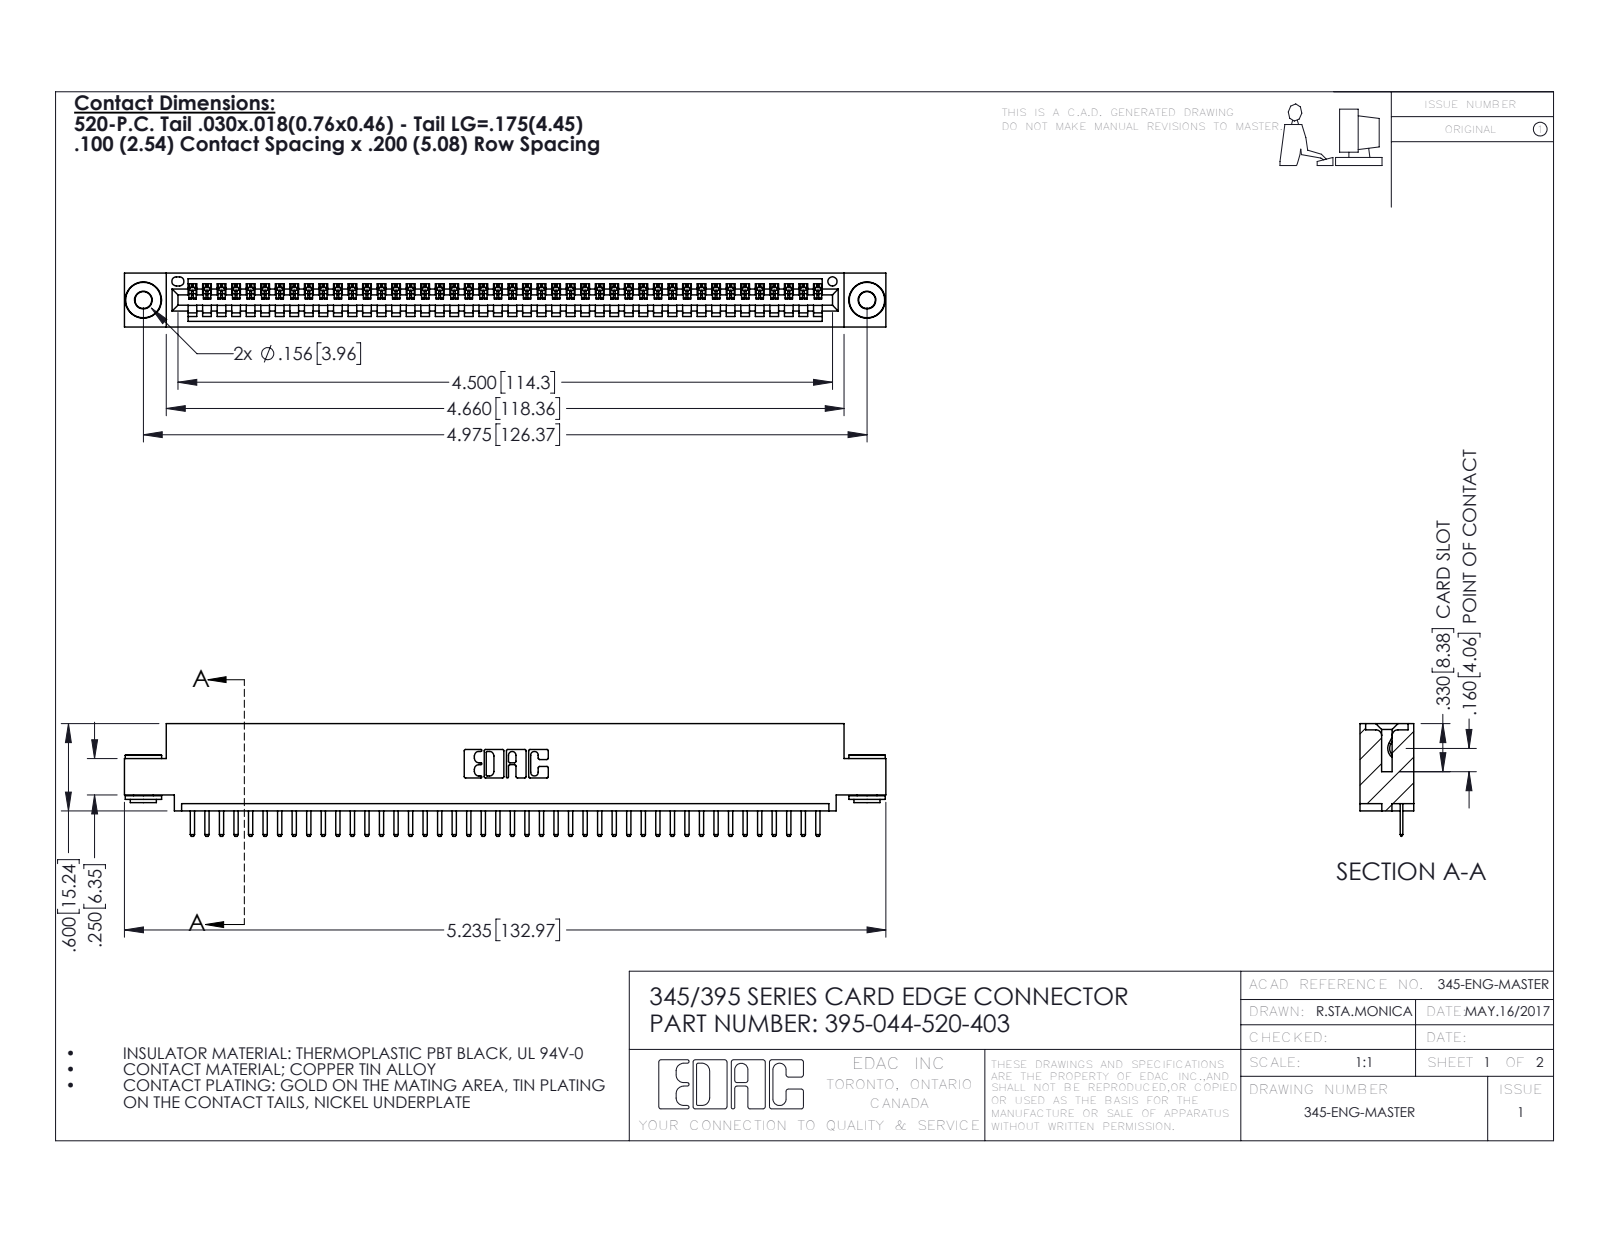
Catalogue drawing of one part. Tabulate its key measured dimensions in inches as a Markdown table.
| quantity | value |
| --- | --- |
| part name | 395-044-520-403; 345-250-002_345-250-002-102; 345-292-001_345-293-120; 345 Part_0.110 Offset - 0.156 Dia-TH |
| STEP written by | SolidWorks 2016 (CONFIG_CONTROL_DESIGN) |
| units | inches |
| bodies | 47 solids, 2896 faces (1942 planar, 946 cylindrical, 8 other) |
| overall size | 5.235 × 0.775 × 0.37 |
| volume | 0.761 in³ |
| surface area | 25.54 in² |
| round holes (diameter × count) | 0.116 × 2, 0.156 × 2, 0.064 × 1 |
| round bosses / shafts (diameter × count) | 0.25 × 2, 0.18 × 2, 0.136 × 2 |
| partial cylindrical surfaces (radius × count) | 0.01 × 90, 0.006 × 88, 0.01 × 22, 0.007 × 6, 0.031 × 6, 0.026 × 3, 0.031 × 2, 0.04 × 2 |
| main face-to-face distances | 0.072, 0.298, 0.37, 0.2, 0.025, 0.098, 0.272, 0.225, 0.072, 0.149 |
| hole center spacings | 0.27, 4.739, 4.975 |
